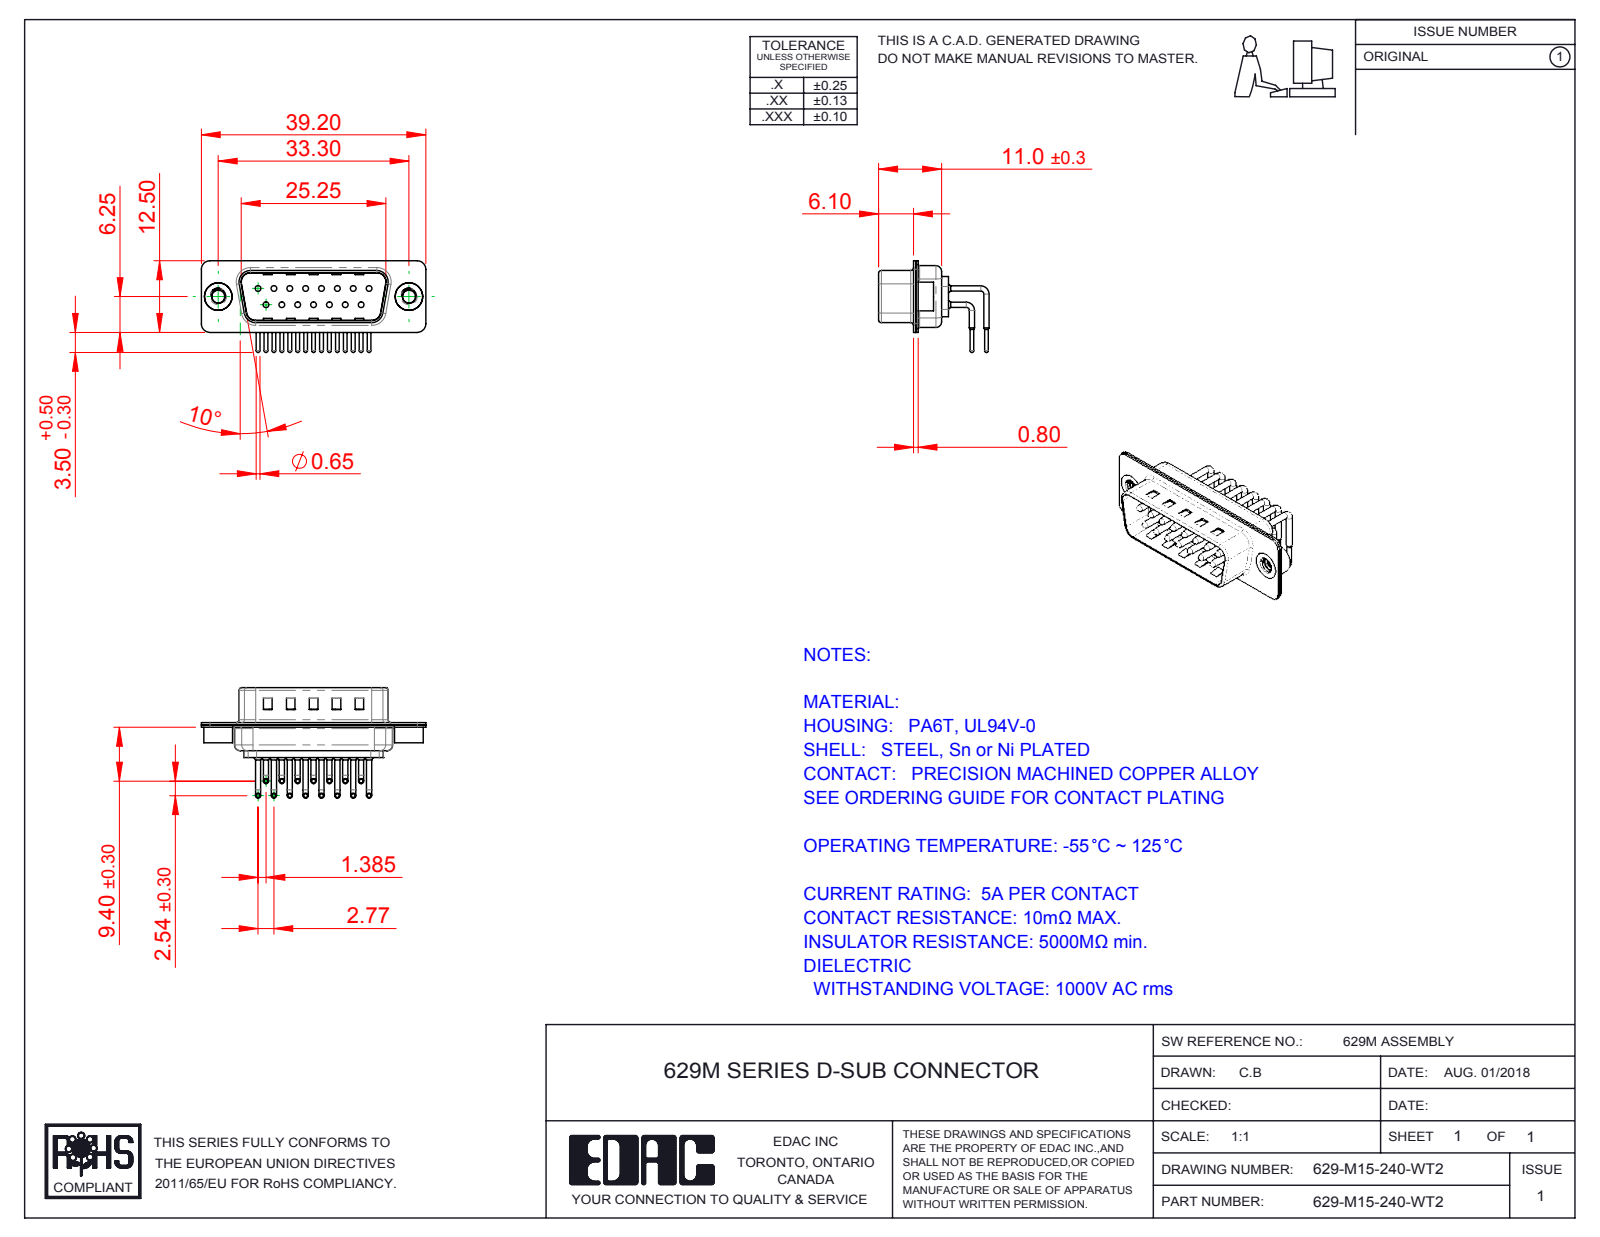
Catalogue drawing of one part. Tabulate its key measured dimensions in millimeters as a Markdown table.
| quantity | value |
| --- | --- |
| part name | 629M Housing_15 Contacts; 629-M15-240-WT2; 629M Shell Rear_15 Contacts; 629M Contact Row 1 (+3 more) |
| STEP written by | SolidWorks 2016 (CONFIG_CONTROL_DESIGN) |
| units | millimeters |
| bodies | 20 solids, 1990 faces (1099 planar, 673 cylindrical, 218 other) |
| overall size | 39.2 × 19.29 × 16 |
| volume | 1 960 mm³ |
| surface area | 5 364 mm² |
| round holes (diameter × count) | 1 × 15, 1.7 × 15, 2 × 15, 2.26 × 2, 4 × 2, 4.8 × 2 |
| round bosses / shafts (diameter × count) | 0.9 × 30, 1.5 × 15, 0.65 × 15, 5 × 2, 4.9 × 2 |
| partial cylindrical surfaces (radius × count) | 1.5 × 16, 1.01 × 15, 2 × 12, 0.5 × 8, 1.6 × 8, 0.25 × 4, 0.6 × 4, 0.65 × 4 |
| main face-to-face distances | 0.4, 0.85, 9.55, 8.7, 1.25, 10.4, 0.8, 1.5, 0.35, 1.9 |
| hole center spacings | 3.16, 2.77, 5.54, 8.31, 11.08, 5.03, 5.04, 7.48 |
